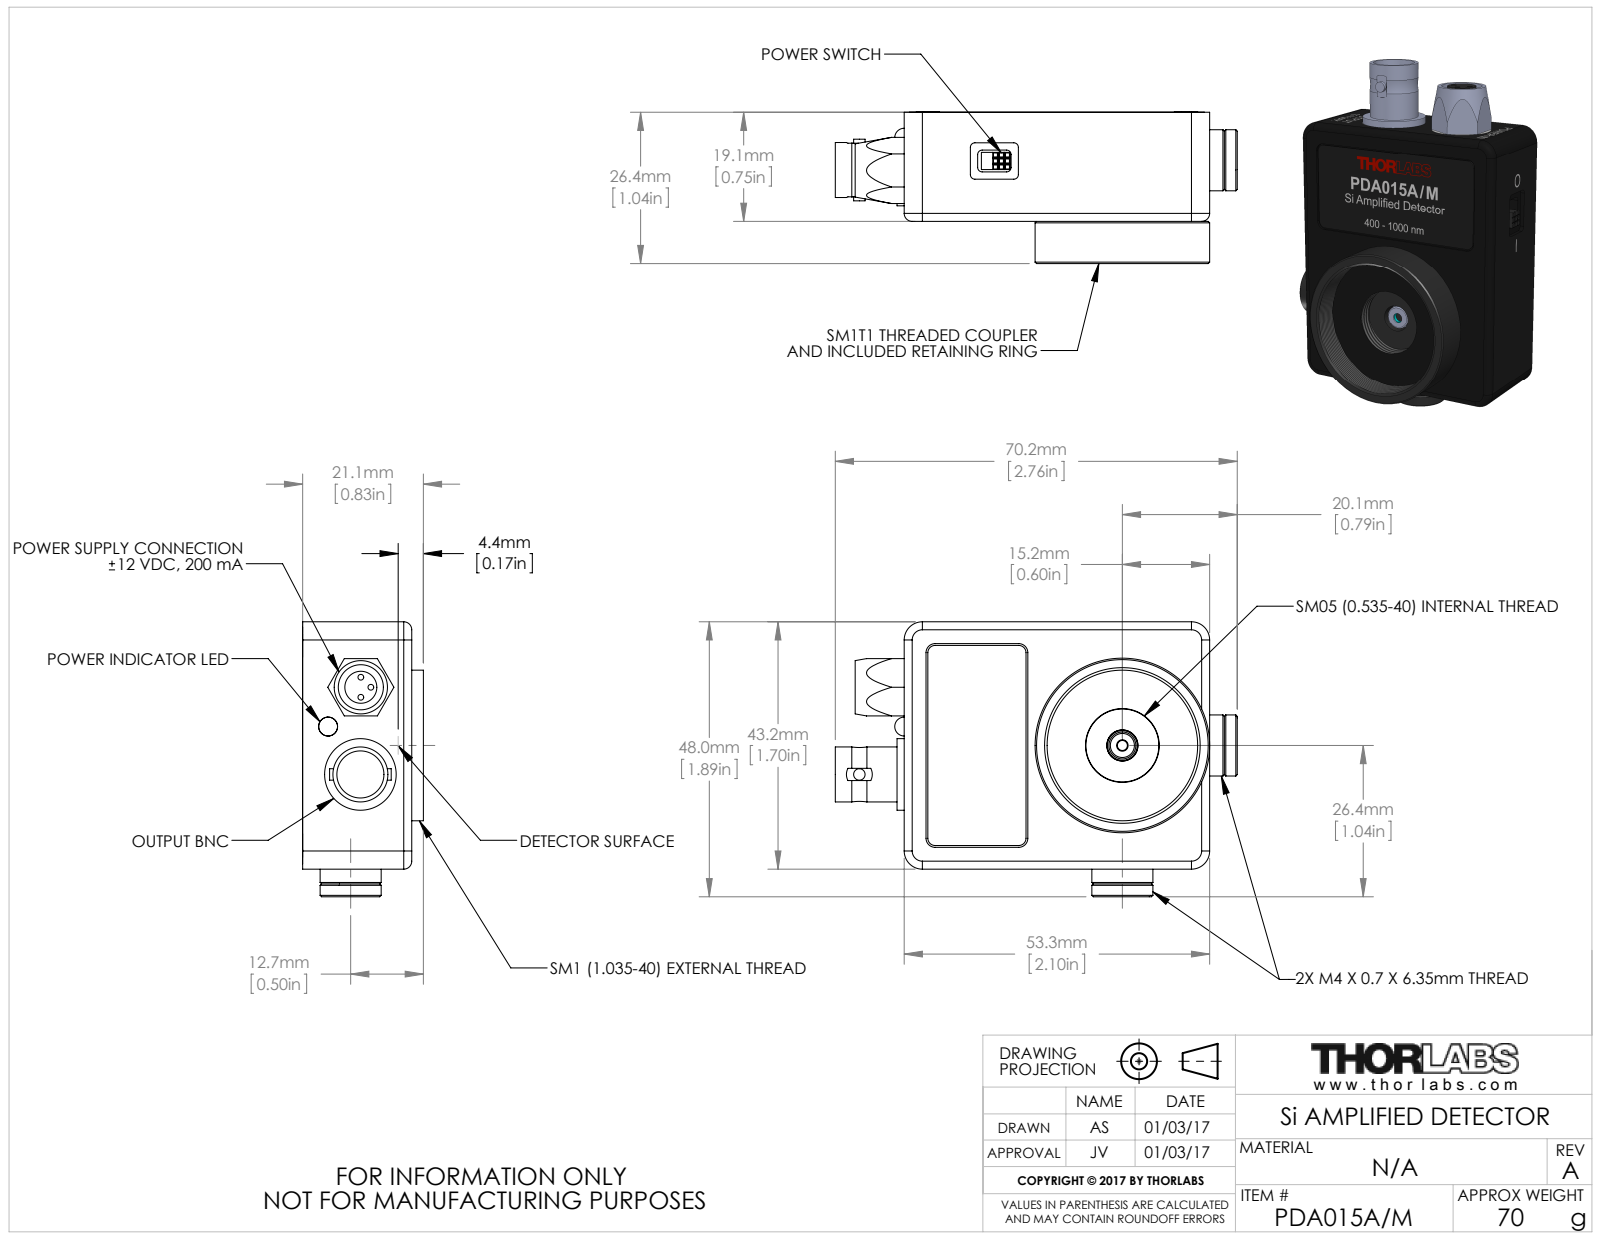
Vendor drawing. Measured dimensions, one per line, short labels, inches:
name: PDA015A_M
written by: SolidWorks 2014 (AUTOMOTIVE_DESIGN)
unit: in
bodies: 0 solids, 329 faces (190 planar, 82 cylindrical, 57 other)
size: 2.763 × 1.89 × 1.041
holes: 3× ⌀0.039, 2× ⌀0.13, 1× ⌀0.069, 1× ⌀0.079, 1× ⌀0.214, 1× ⌀0.31, 1× ⌀0.324, 1× ⌀0.507, 1× ⌀1.035
bosses: 2× ⌀0.42, 1× ⌀1.2, 1× ⌀0.492, 1× ⌀0.378, 1× ⌀0.22, 1× ⌀0.079
rounds: 8× R0.031, 4× R0.05, 4× R0.055, 4× R0.095, 4× R0.1, 4× R0.125, 2× R0.063, 2× R0.063
face distances: 0.751, 1.7, 0.731, 0.02, 0.743, 2.1, 0.831, 0.1, 0.088, 0.08
hole spacings: 0.069, 0.097, 0.138, 0.21, 0.339, 0.406, 0.424, 0.474
